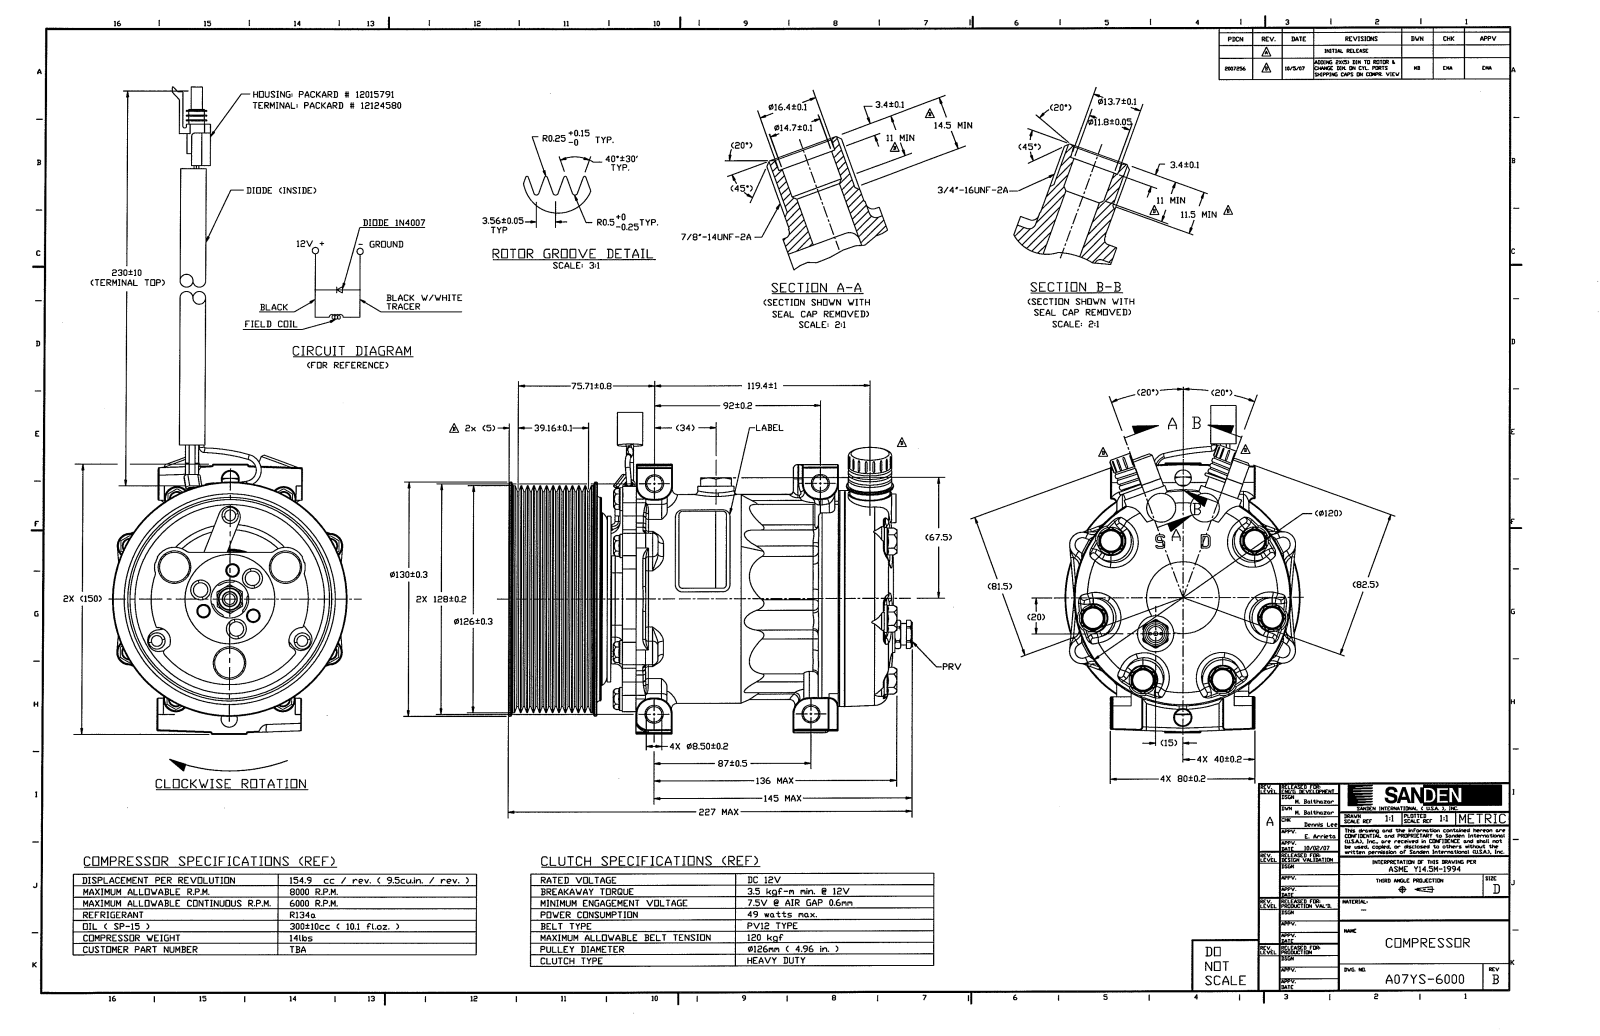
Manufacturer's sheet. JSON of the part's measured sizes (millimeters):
{"part_name": "40702", "step_written_by": "SolidWorks 2007 (CONFIG_CONTROL_DESIGN)", "units": "millimeters", "bodies": {"solids": 3, "faces": 2586, "planar": 603, "cylindrical": 805, "other": 1178}, "overall_size": [294.21, 223.59, 130], "volume_mm3": 2205000, "surface_area_mm2": 274616, "round_holes": [[8.5, 12], [8, 6], [11.9, 6], [5.1, 3], [6.35, 3], [7.5, 3], [9, 2], [3, 1], [4, 1], [9.53, 1], [11.8, 1], [12.9, 1]], "round_bosses_or_shafts": [[12.9, 8], [15.3, 6], [16, 5], [2.7, 5], [18, 3], [11, 3], [9, 3], [5, 3]], "partial_cylinders_radius": [[0.5, 75], [1.5, 48], [2, 36], [7, 36], [5, 15], [3, 13], [19, 7], [4, 6]], "face_to_face_distances": [44.94, 2, 44.84, 39.14, 49.74, 4.8, 45.54, 0.6, 4.2, 6.4], "hole_center_spacings": [62.85, 88.89, 42.09, 16, 31.48, 36.77, 59, 66.7]}
